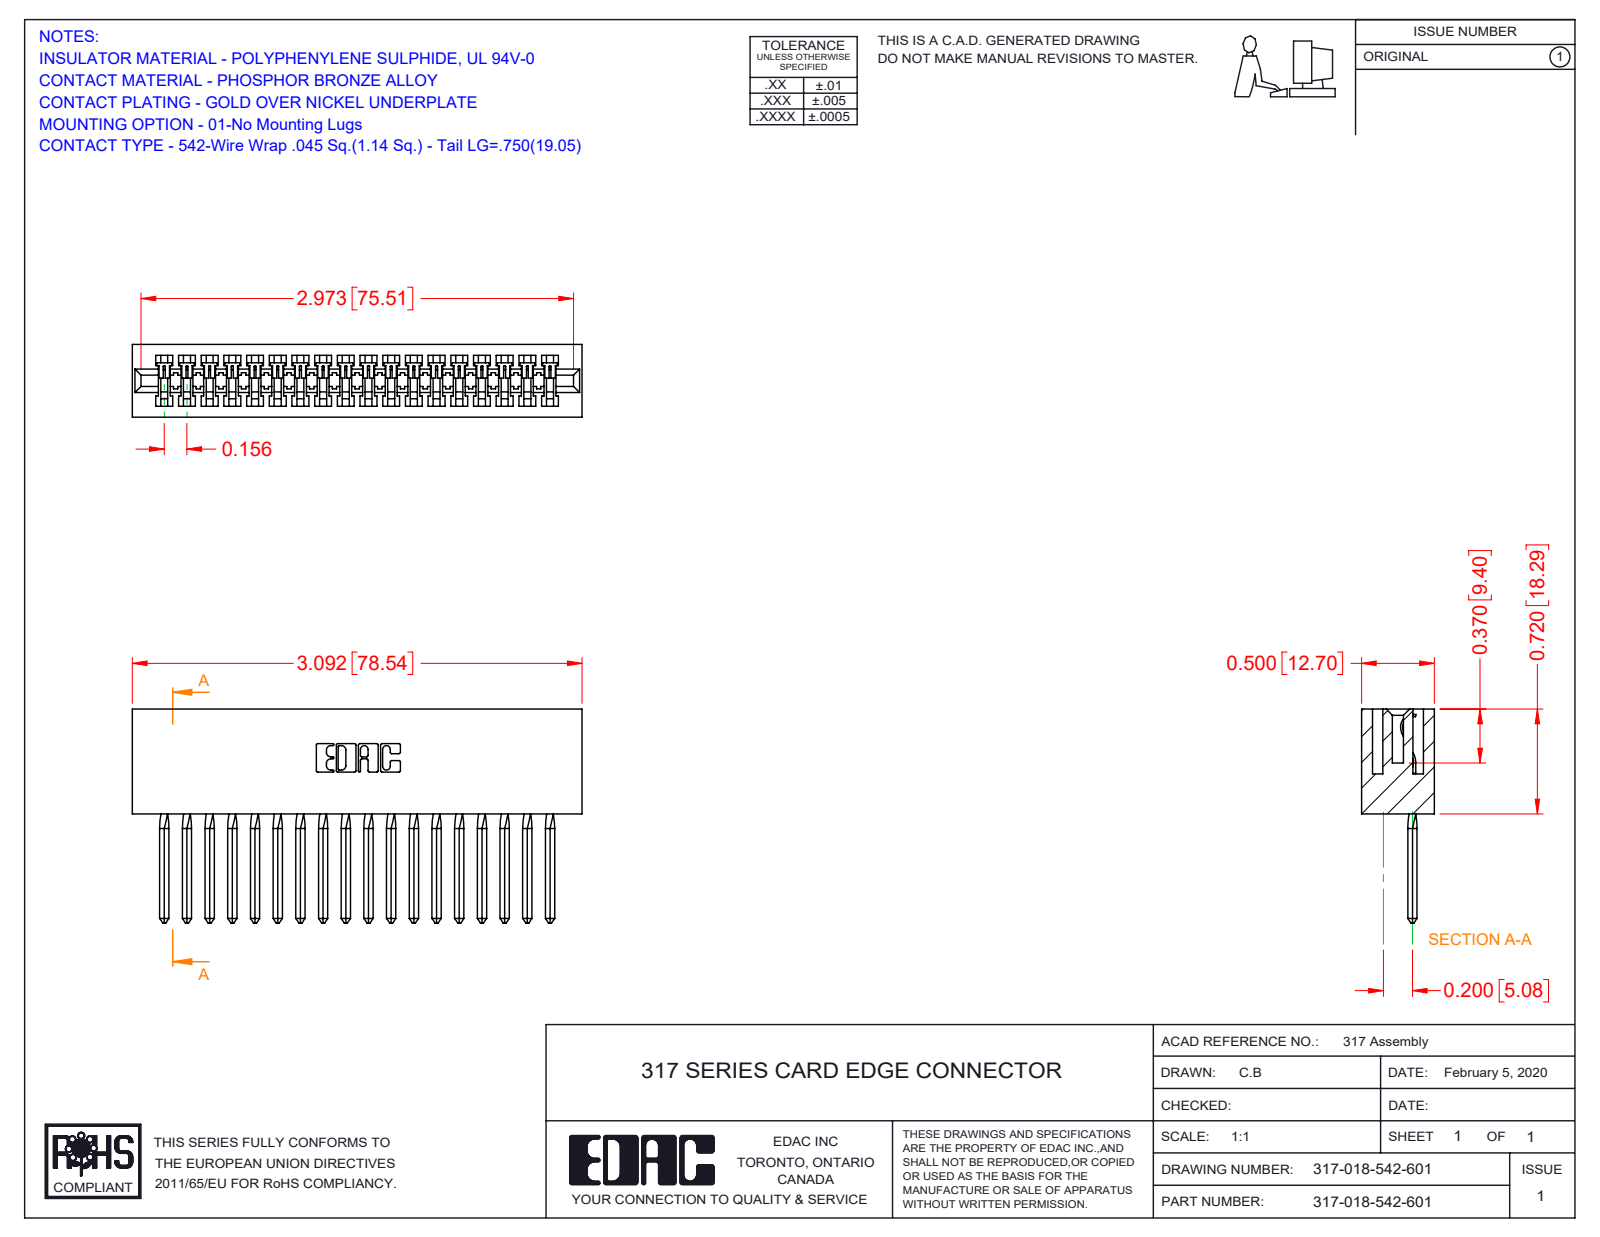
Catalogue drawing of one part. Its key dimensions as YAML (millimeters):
part_name: "317 Part_Lugless; 317-018-542-601; 317-290-003_542"
step_written_by: "SolidWorks 2016 (CONFIG_CONTROL_DESIGN)"
units: millimeters
bodies: {solids: 19, faces: 1440, planar: 1202, cylindrical: 166, other: 72}
overall_size: [78.5, 37.3, 12.7]
volume: 13100
surface_area: 15460
partial_cylinders:
  - {radius: 0.2, count: 36}
  - {radius: 0.3, count: 22}
  - {radius: 0.2, count: 6}
  - {radius: 0.8, count: 6}
  - {radius: 0.7, count: 3}
  - {radius: 1.9, count: 1}
  - {radius: 2.3, count: 1}
  - {radius: 2.5, count: 1}
face_to_face_distances: [12.7, 1.9, 10.8, 2.8, 8.9, 3.5, 4, 18.3, 1.7, 5.4]
